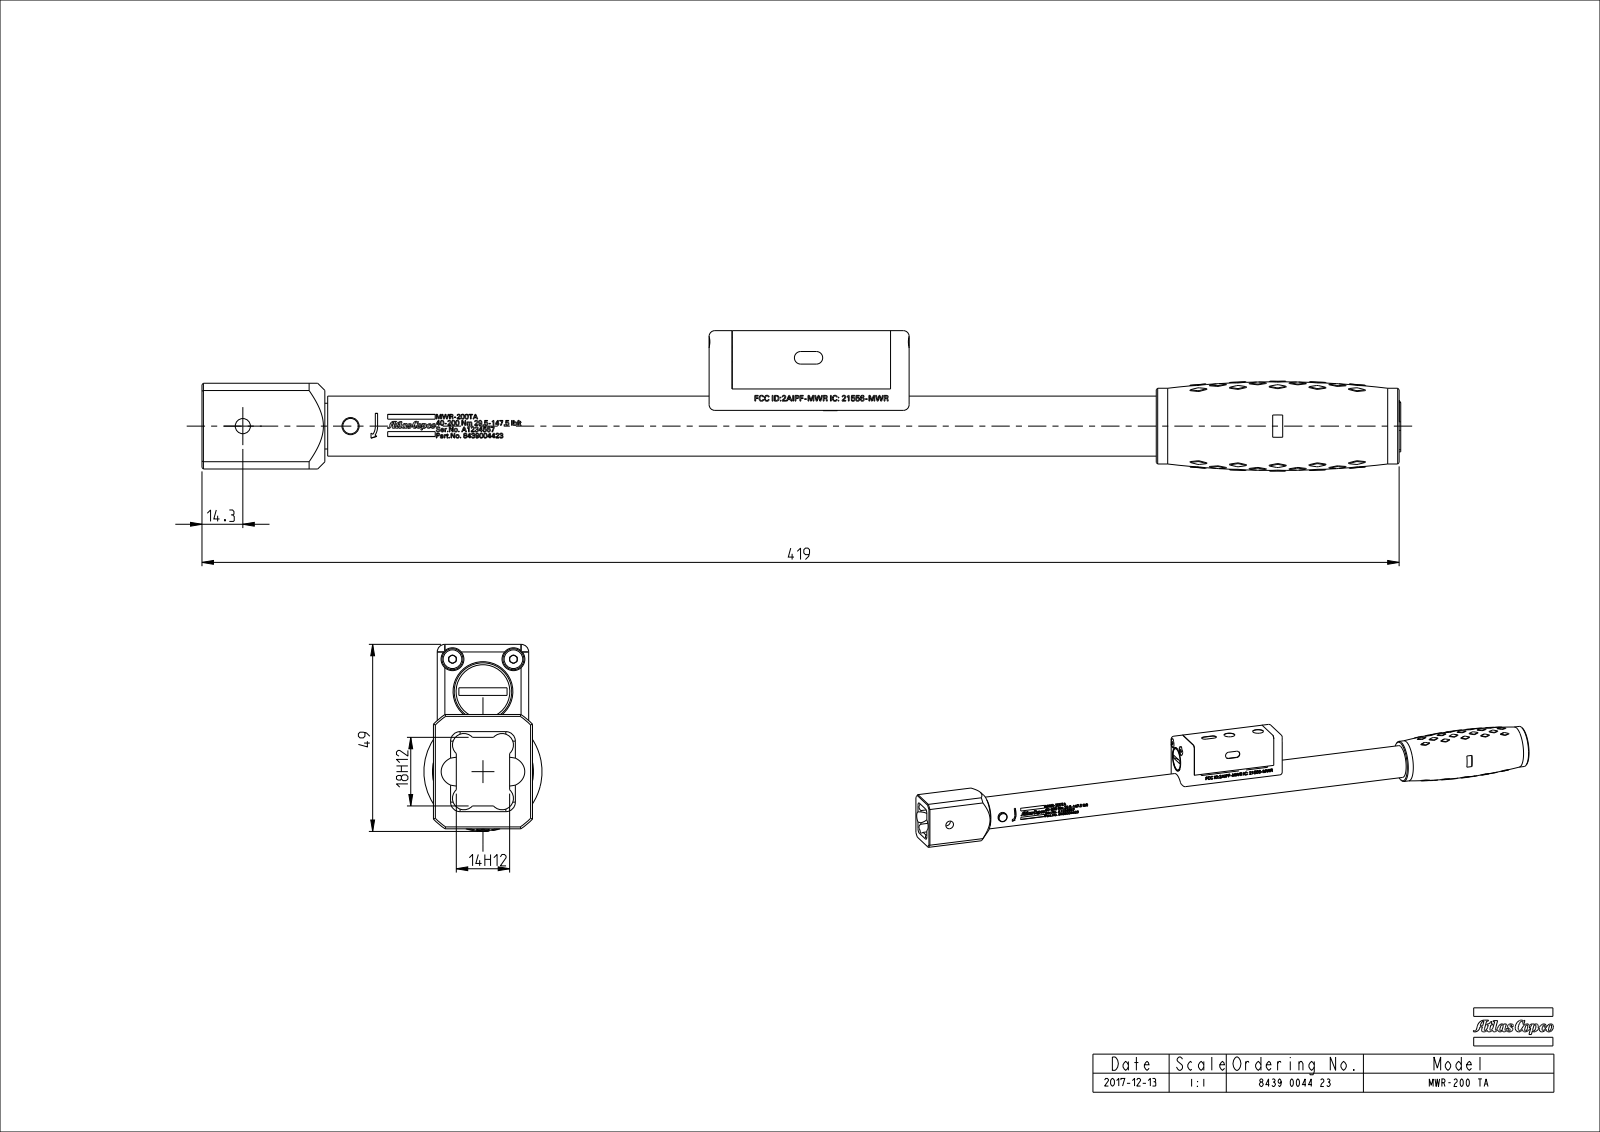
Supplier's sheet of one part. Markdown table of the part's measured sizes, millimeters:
| quantity | value |
| --- | --- |
| part name | 8439004423 |
| STEP written by | SolidWorks 2016 (AUTOMOTIVE_DESIGN) |
| units | millimeters |
| bodies | 0 solids, 486 faces (106 planar, 81 cylindrical, 299 other) |
| overall size | 419 × 49.21 × 31 |
| round holes (diameter × count) | 6 × 2, 7 × 2, 5.3 × 1, 15.1 × 1, 16.5 × 1, 26.5 × 1 |
| round bosses / shafts (diameter × count) | 5.5 × 2, 21 × 1, 14.1 × 1, 6 × 1 |
| partial cylindrical surfaces (radius × count) | 2 × 12, 1 × 6, 2.25 × 3, 0.5 × 2, 3 × 2, 11 × 1, 18 × 1 |
| main face-to-face distances | 24, 1, 25, 6, 26, 18.4, 30, 48.4, 20, 5 |
| hole center spacings | 11.67, 30.57, 16, 20, 21 |
